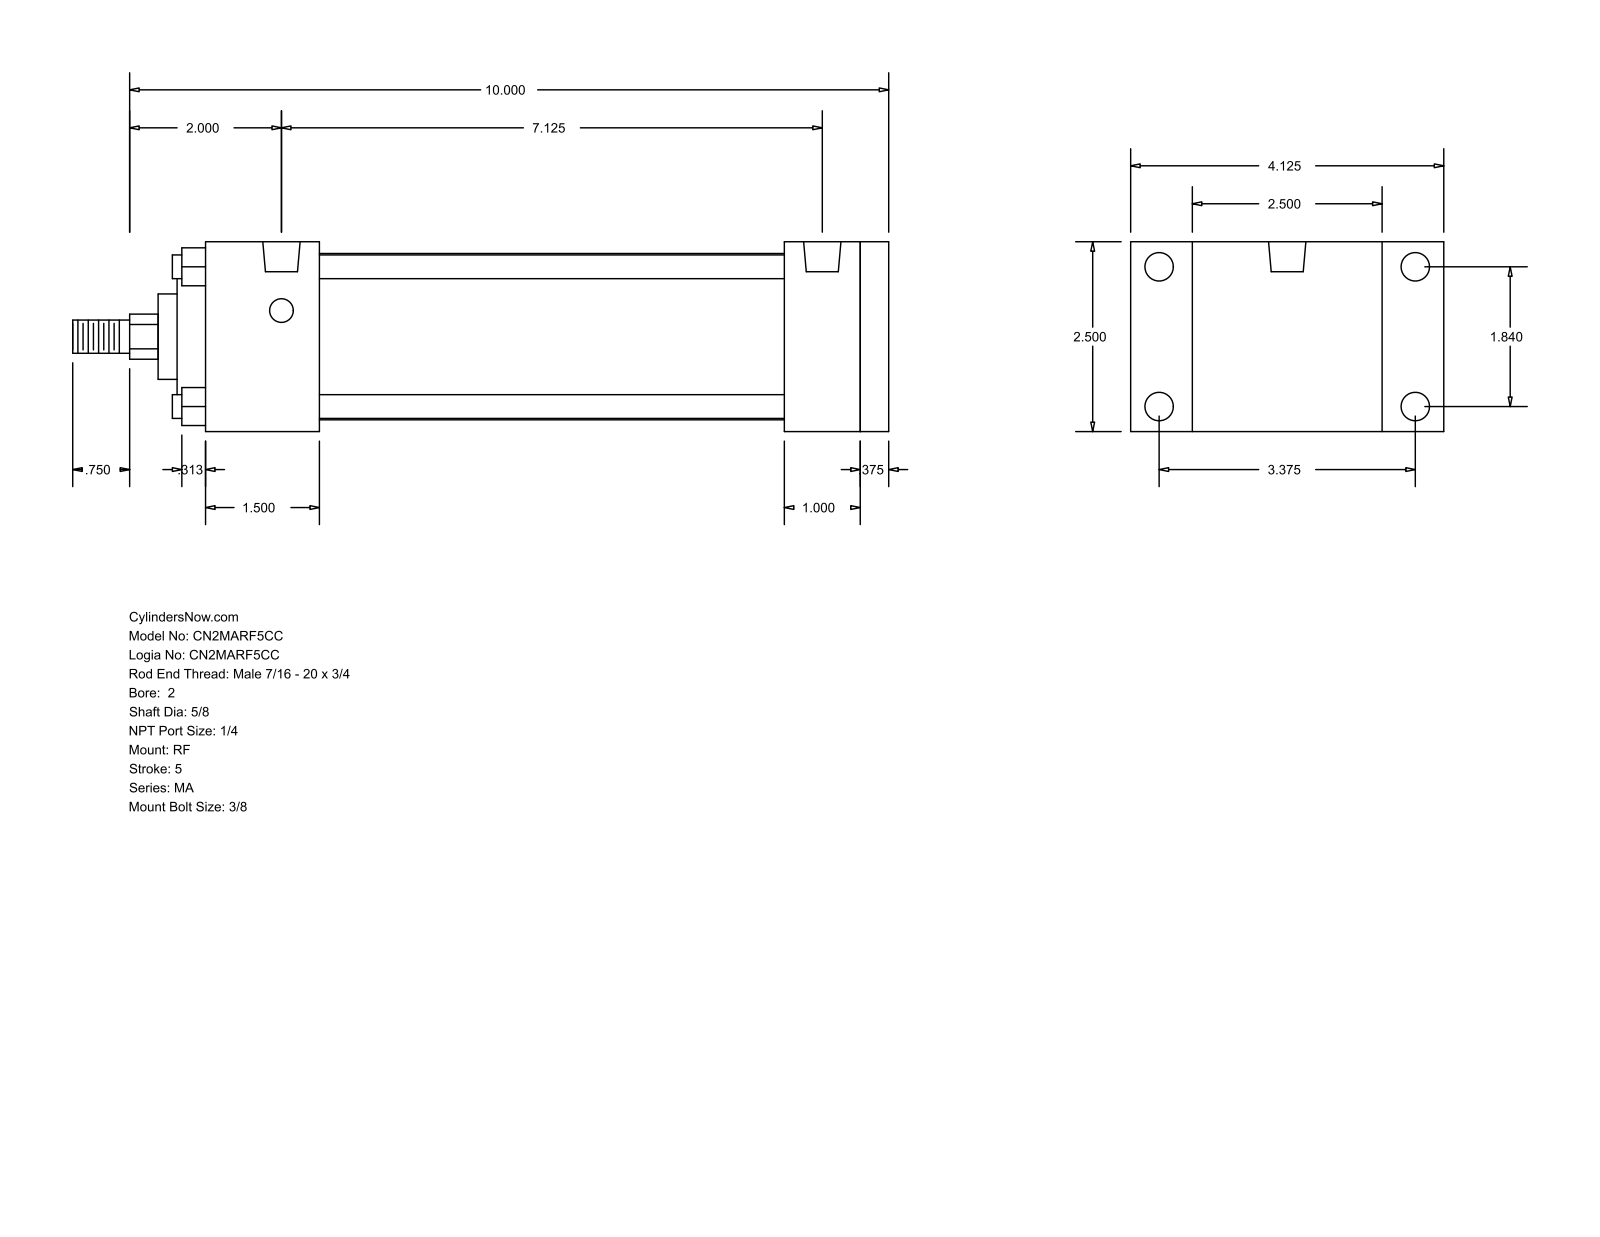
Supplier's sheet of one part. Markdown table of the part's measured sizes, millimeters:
| quantity | value |
| --- | --- |
| part name | MA_RF__0200_0.625 |
| STEP written by | GSSL Pune (CONFIG_CONTROL_DESIGN) |
| units | millimeters |
| bodies | 0 solids, 94 faces (65 planar, 29 cylindrical, 0 other) |
| overall size | 273.05 × 104.78 × 63.5 |
| round holes (diameter × count) | 7.94 × 4, 9.53 × 4, 12.49 × 2 |
| round bosses / shafts (diameter × count) | 7.94 × 4, 55.63 × 1, 50.8 × 1, 28.57 × 1, 15.88 × 1, 11.11 × 1 |
| partial cylindrical surfaces (radius × count) | 7.54 × 1 |
| main face-to-face distances | 63.5, 9.53, 25.4, 38.1, 238.12, 219.07, 34.93, 228.6, 180.97, 190.5 |
| hole center spacings | 46.74, 85.72, 97.63, 180.98 |
